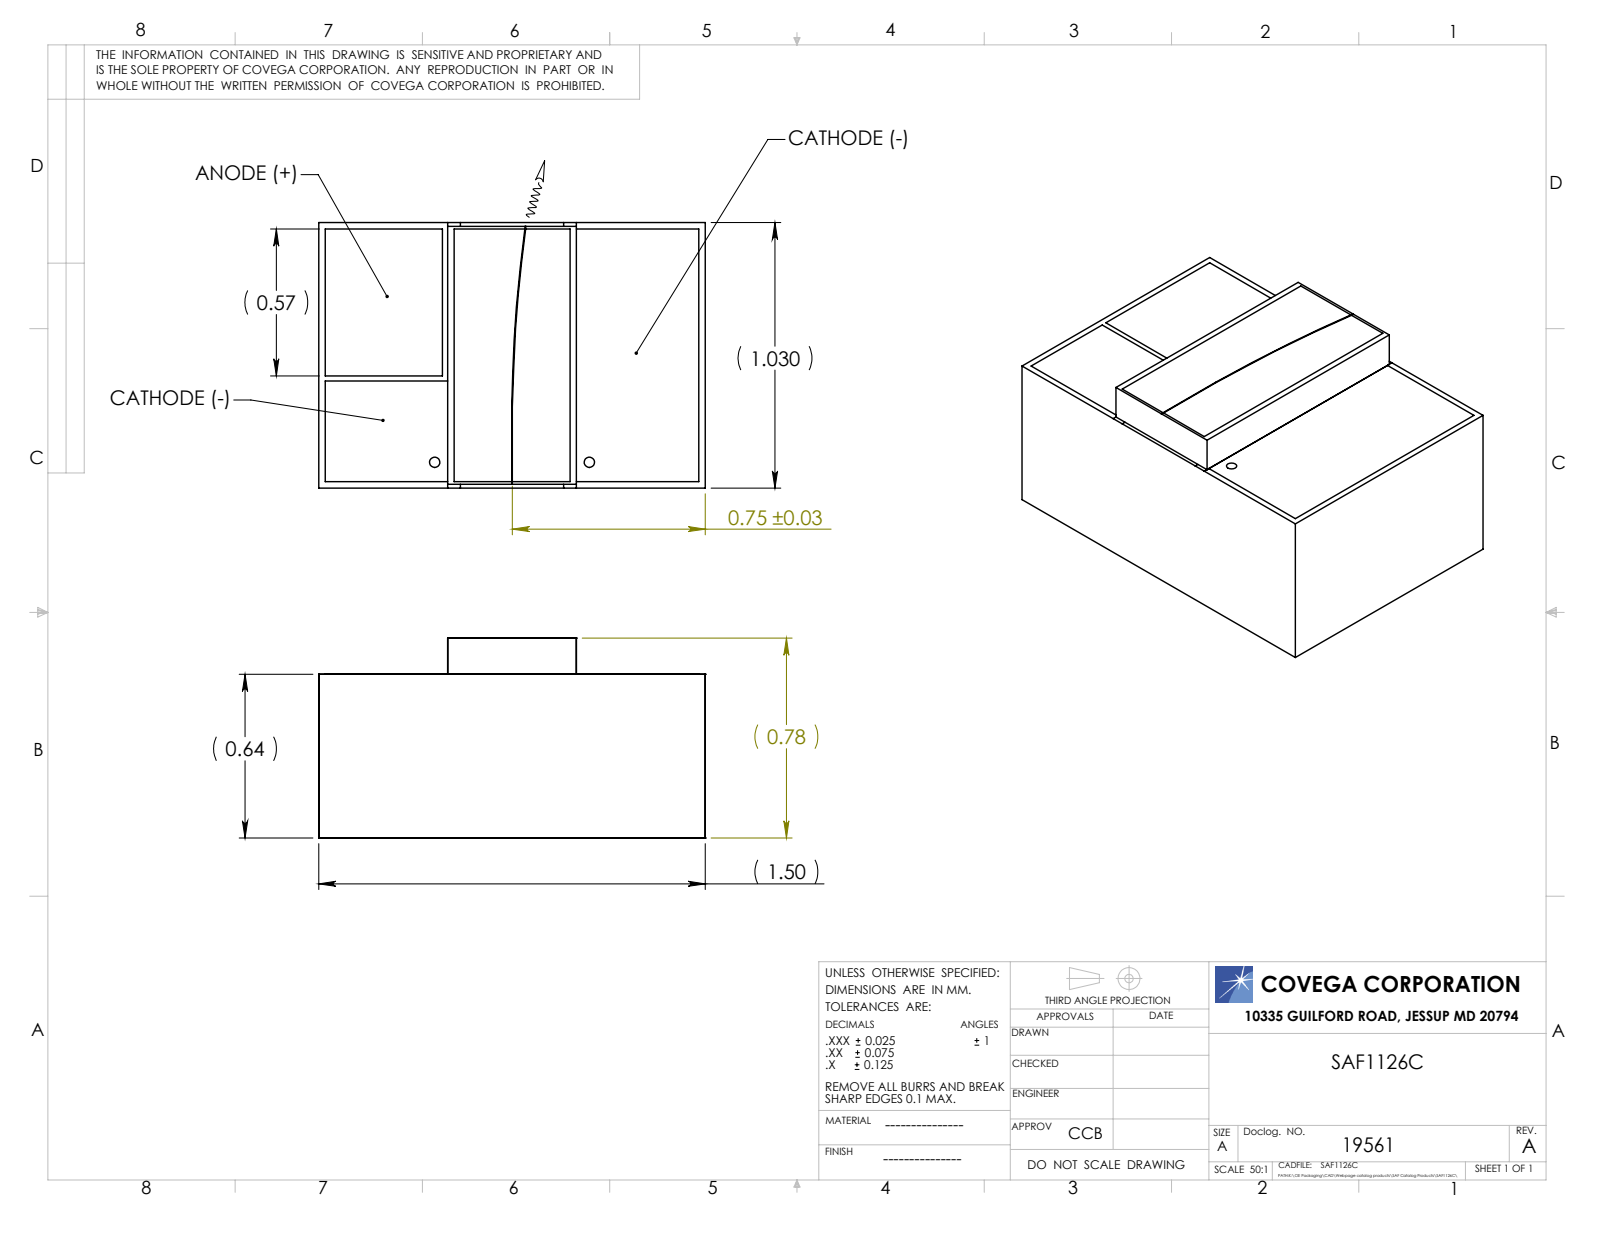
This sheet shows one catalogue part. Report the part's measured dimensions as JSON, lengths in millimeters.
{"part_name": "32068-000; 19561-E0W; 31002-XXX", "step_written_by": "SolidWorks 2009 (CONFIG_CONTROL_DESIGN)", "units": "millimeters", "bodies": {"solids": 2, "faces": 26, "planar": 26, "cylindrical": 0, "other": 0}, "overall_size": [1.5, 1.03, 0.78], "volume_mm3": 1, "surface_area_mm2": 8, "face_to_face_distances": [0.64, 1.03, 1.5, 0.78, 0.5, 1, 1.01, 0.99]}
